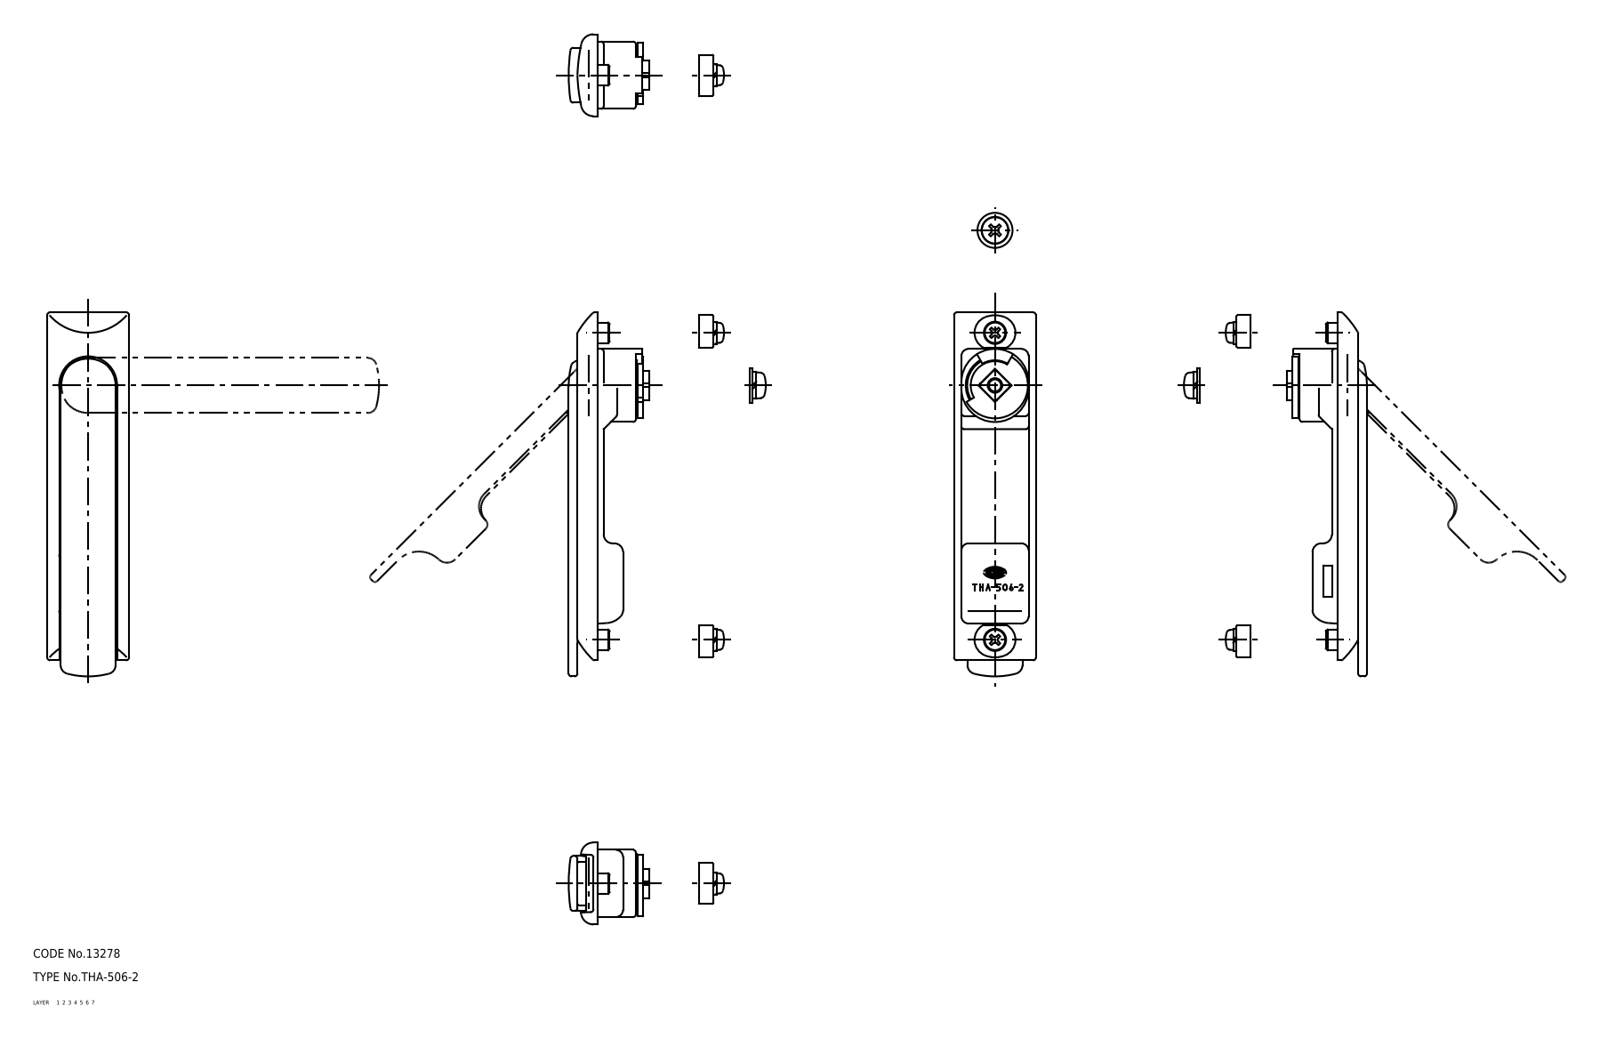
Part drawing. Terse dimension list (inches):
name: THA_506_2
written by: SolidWorks 2003240 (AUTOMOTIVE_DESIGN)
unit: in
bodies: 10 solids, 407 faces (138 planar, 165 cylindrical, 104 other)
size: 4.902 × 1.293 × 1.102
volume: 2.046 in³; area: 37.39 in²
holes: 3× ⌀0.157, 2× ⌀0.165, 2× ⌀0.299, 1× ⌀0.197, 1× ⌀0.469, 1× ⌀0.63, 1× ⌀0.783
bosses: 2× ⌀0.276, 1× ⌀0.787, 1× ⌀0.744, 1× ⌀0.507, 1× ⌀0.472, 1× ⌀0.465, 1× ⌀0.362
rounds: 32× R0.039, 7× R0.118, 6× R0.059, 5× R0.157, 4× R0.098, 4× R0.226, 3× R0.197, 2× R0.012
face distances: 0.079, 0.02, 0.26, 0.76, 0.181, 0.354, 0.843, 0.161, 0.35, 0.098
hole spacings: 0.709, 3.425, 4.134
